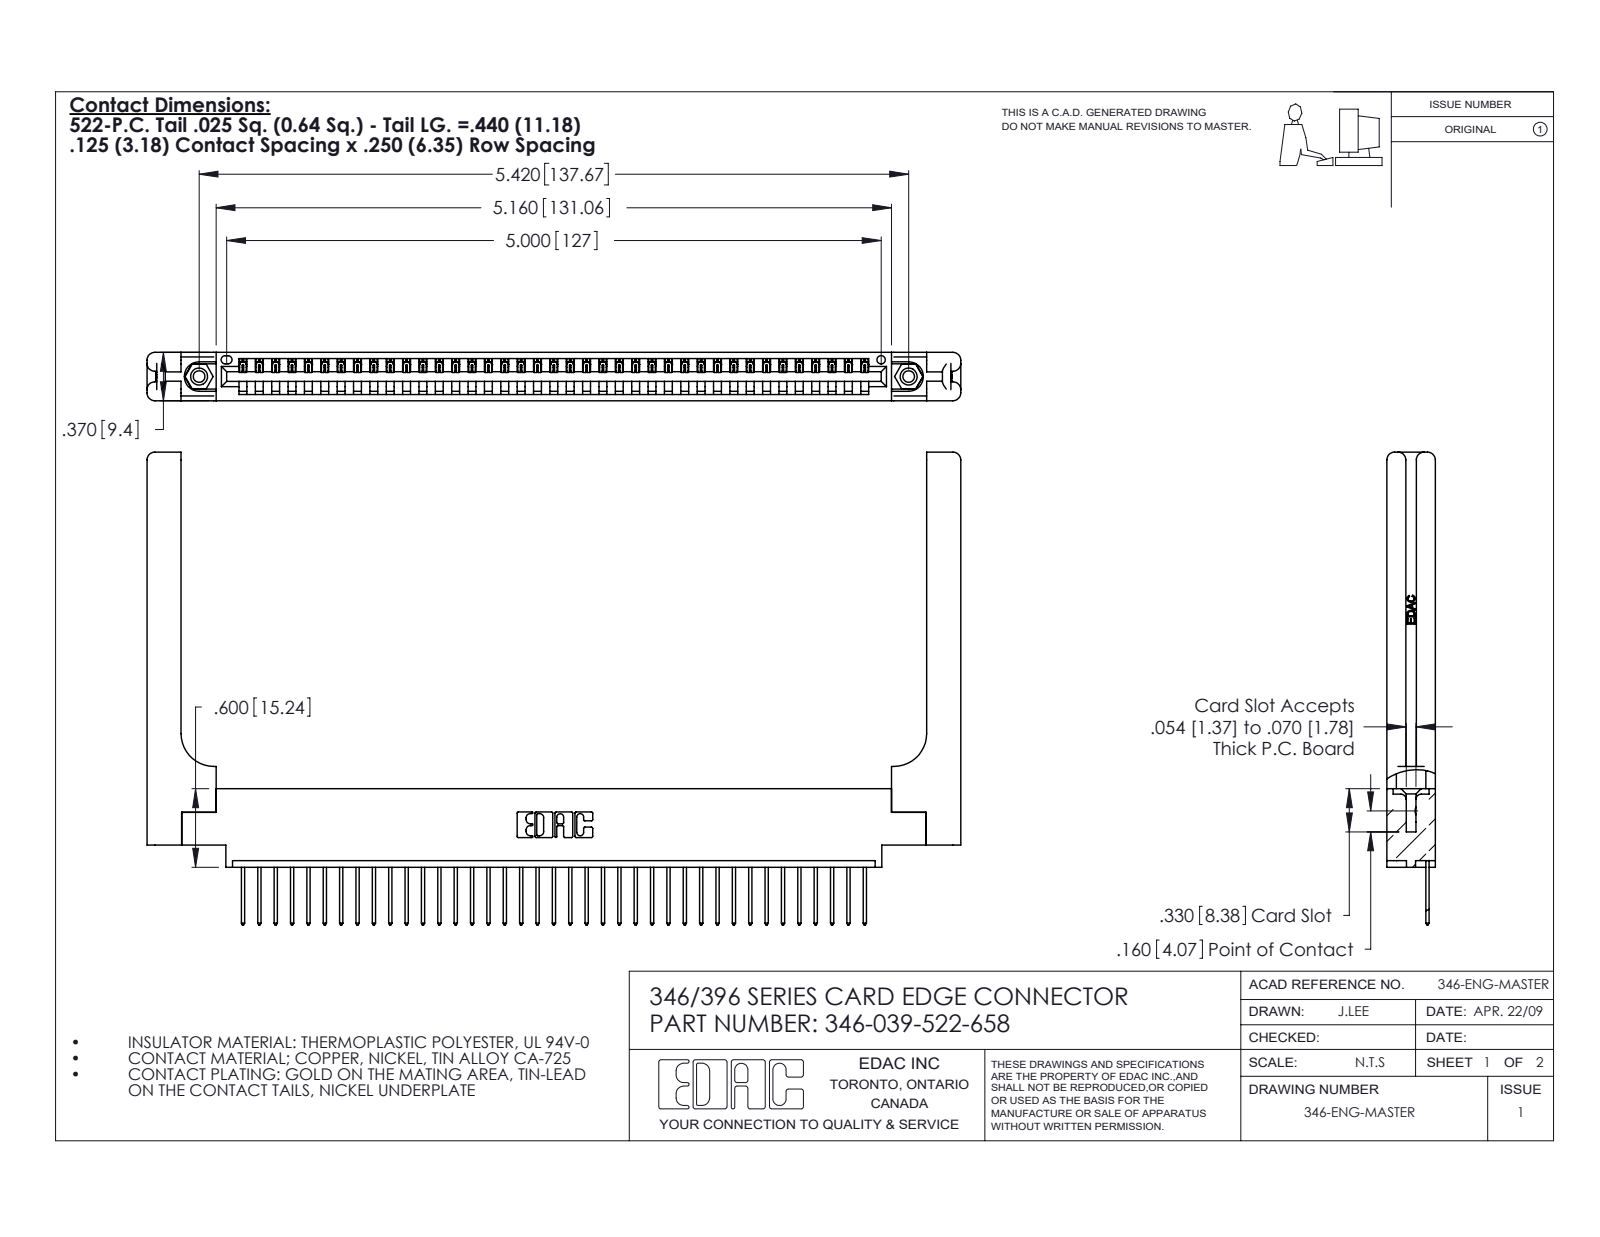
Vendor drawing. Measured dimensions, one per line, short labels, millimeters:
name: 345-250-001_345-250-001-102; 345-292-001_345-293-122; 346-039-522-658; 346 Part_0.170 Offset - 0.156 Dia-TH (+1 more)
written by: SolidWorks 2020 (CONFIG_CONTROL_DESIGN)
unit: mm
bodies: 44 solids, 2658 faces (1802 planar, 796 cylindrical, 60 other)
size: 157.9 × 91.7 × 9.4
volume: 22 450 mm³; area: 24 130 mm²
holes: 2× ⌀2.3, 2× ⌀3.2, 2× ⌀4, 1× ⌀1.6
bosses: 2× ⌀3.9
rounds: 78× R0.2, 78× R0.3, 22× R0.3, 16× R1.5, 6× R0.2, 6× R0.8, 3× R0.7, 2× R0.8
face distances: 9.4, 1.2, 8.2, 1.8, 3.8, 3.8, 6.4, 7.6, 0.6, 5.6
hole spacings: 6.2, 132.4, 137.7
